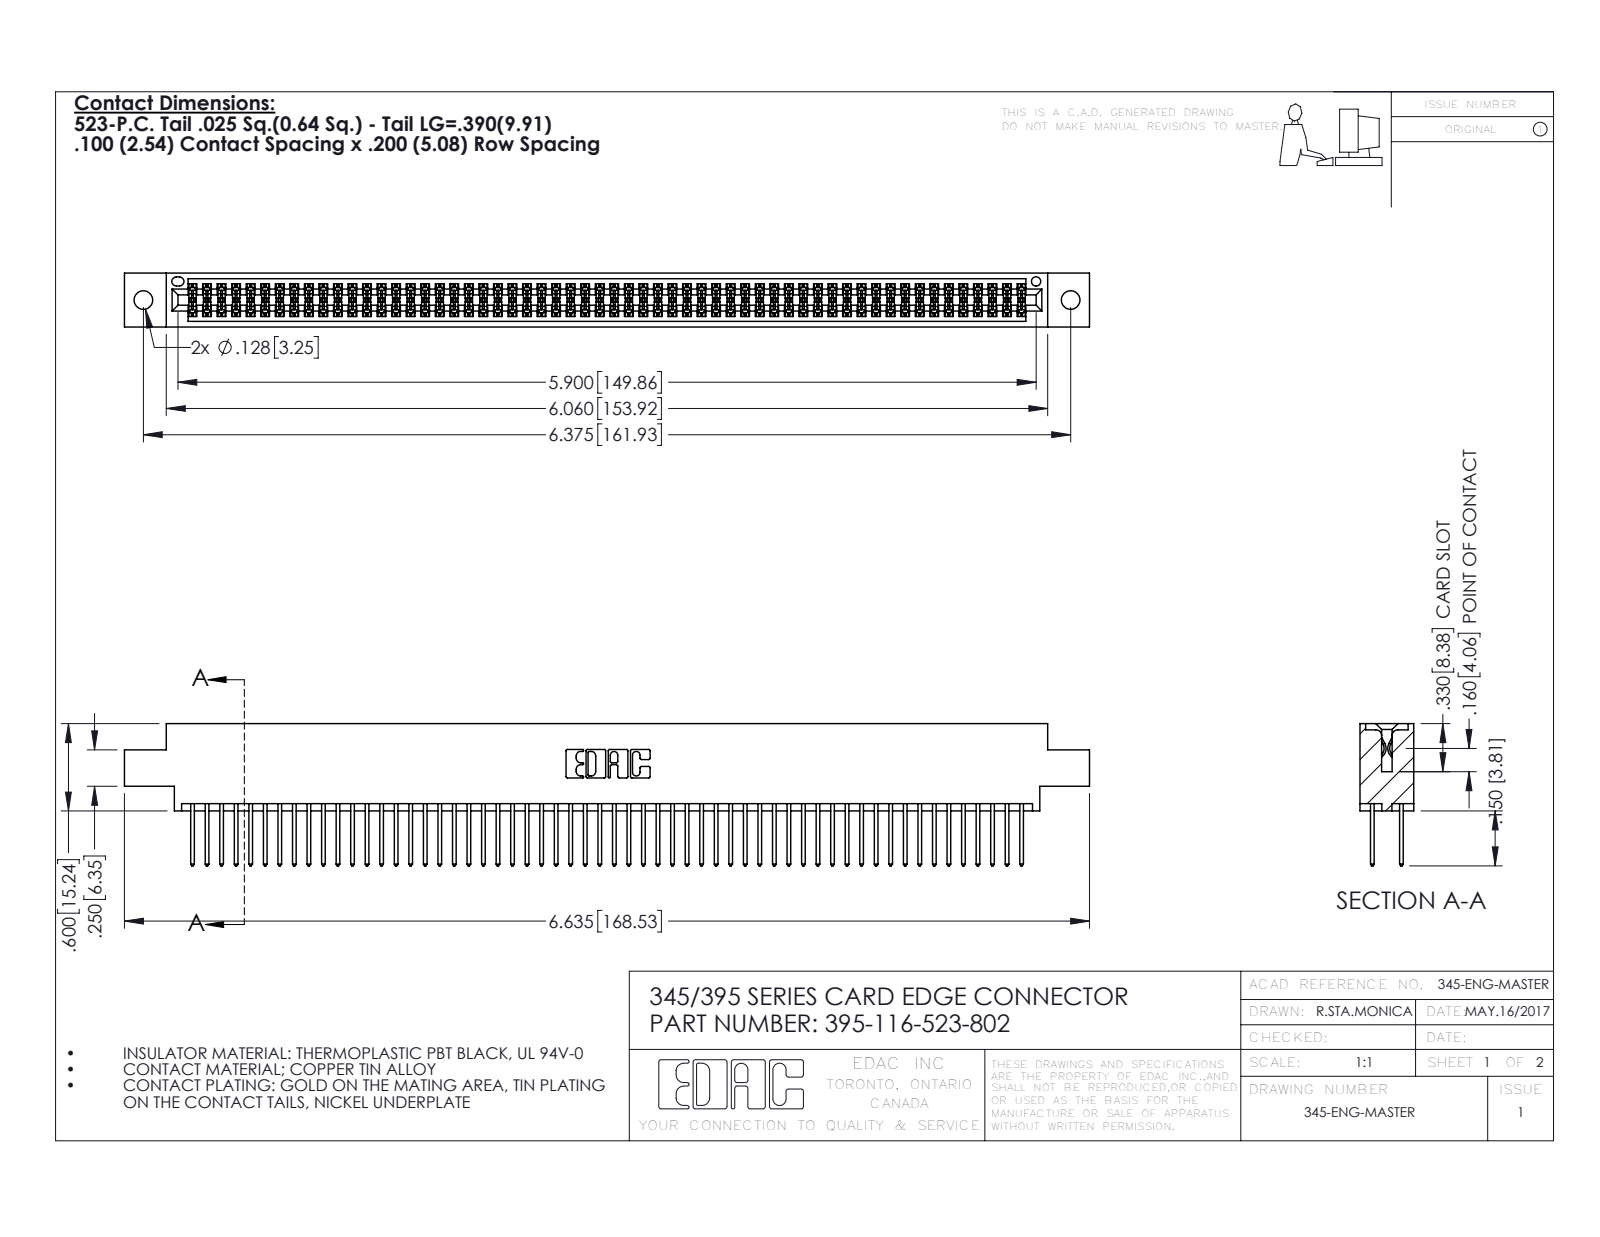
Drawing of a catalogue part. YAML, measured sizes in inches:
part_name: "395-116-523-802; 345 Part_0.170 Offset - 0.128 Dia; 345-292-001_345-293-123"
step_written_by: "SolidWorks 2016 (CONFIG_CONTROL_DESIGN)"
units: inches
bodies: {solids: 117, faces: 5930, planar: 3912, cylindrical: 2018, other: 0}
overall_size: [6.635, 0.977, 0.37]
volume: 1.013
surface_area: 39.98
round_holes:
  - {diameter: 0.128, count: 2}
  - {diameter: 0.064, count: 1}
partial_cylinders:
  - {radius: 0.006, count: 174}
  - {radius: 0.01, count: 116}
  - {radius: 0.01, count: 22}
  - {radius: 0.007, count: 6}
  - {radius: 0.031, count: 6}
  - {radius: 0.026, count: 3}
  - {radius: 0.014, count: 2}
  - {radius: 0.019, count: 2}
face_to_face_distances: [0.298, 0.072, 0.2, 0.098, 0.272, 0.025, 0.37, 0.225, 0.175, 0.149]
hole_center_spacings: [0.27, 6.139, 6.375]
